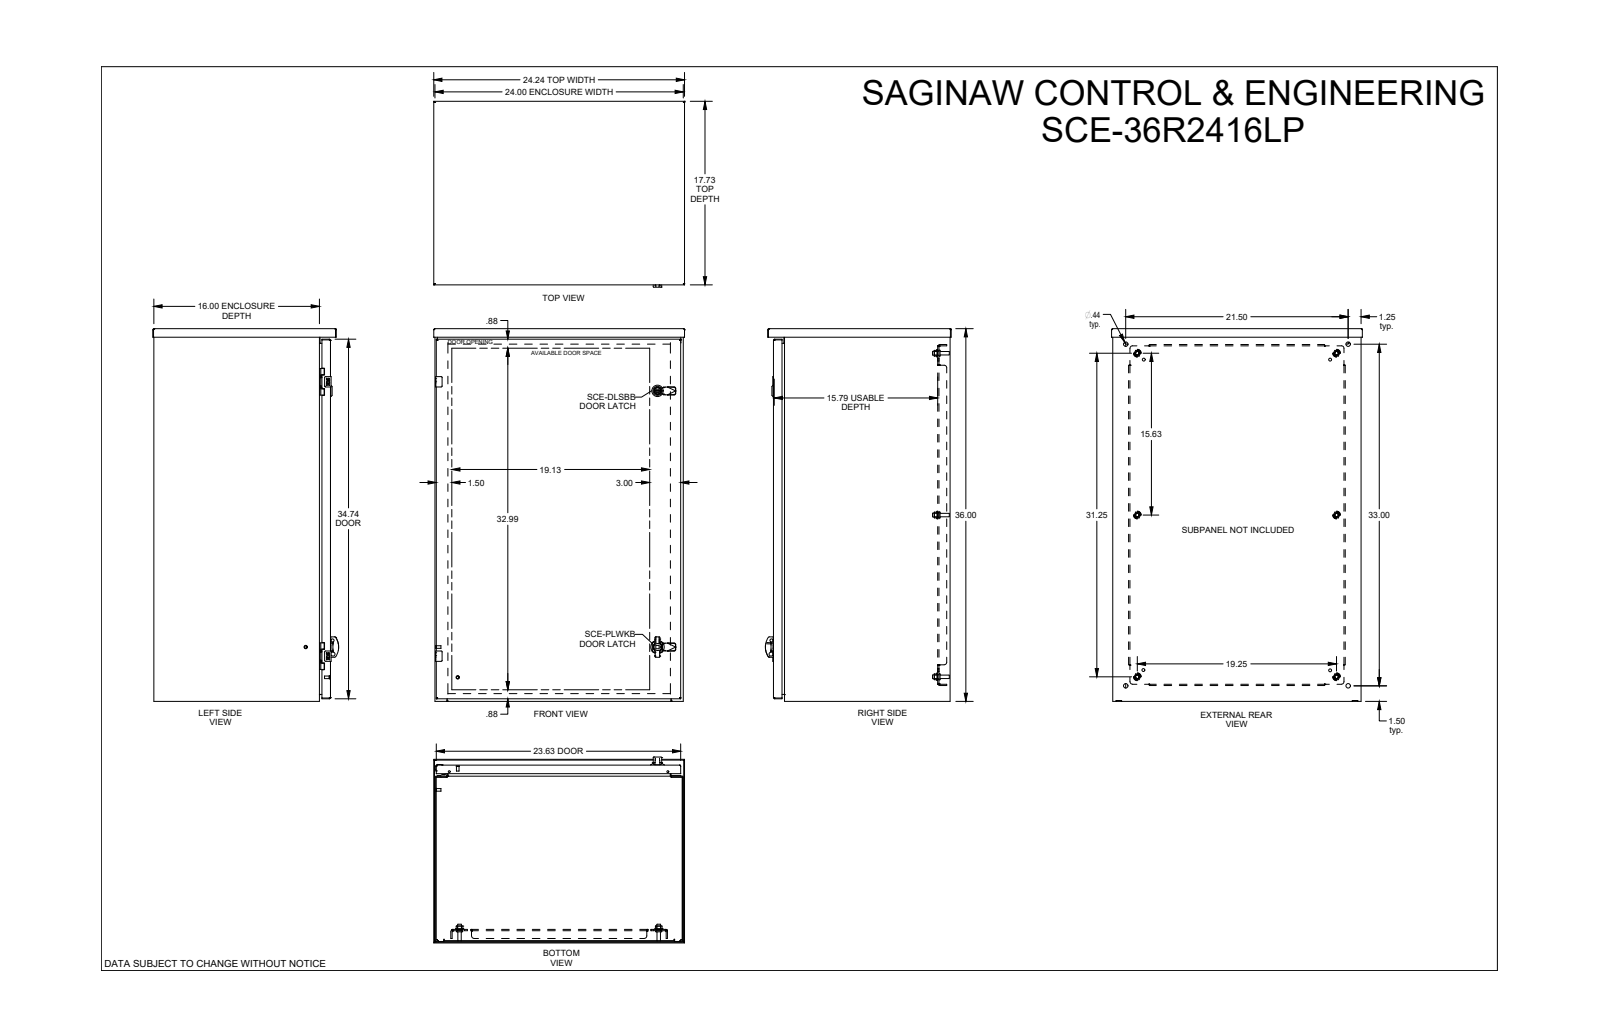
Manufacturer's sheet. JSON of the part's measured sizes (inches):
{"part_name": "SCE-36R2416LP", "step_written_by": "SolidWorks 2019 (CONFIG_CONTROL_DESIGN)", "units": "inches", "bodies": {"solids": 0, "faces": 2607, "planar": 1214, "cylindrical": 875, "other": 518}, "overall_size": [36, 24.236, 17.957], "round_holes": [[0.367, 6], [0.5, 6], [0.172, 4], [0.205, 4], [0.244, 4], [0.266, 4], [0.281, 4], [0.375, 4], [0.438, 4], [0.04, 2], [0.156, 2], [0.188, 2]], "round_bosses_or_shafts": [[0.366, 6], [0.332, 6], [0.17, 6], [0.25, 4], [0.24, 4], [0.196, 3], [0.866, 2], [0.802, 2]], "partial_cylinders_radius": [[0.015, 70], [0.012, 60], [0.06, 46], [0.01, 38], [0.02, 24], [0.117, 19], [0.042, 17], [0.03, 15]], "face_to_face_distances": [0.075, 0.075, 23.925, 16.918, 16.993, 17.068, 16.993, 0.125, 1, 15.918], "hole_center_spacings": [26.5, 0.494, 0.875, 1.426, 15.625, 16.538, 20.394, 24.793]}
